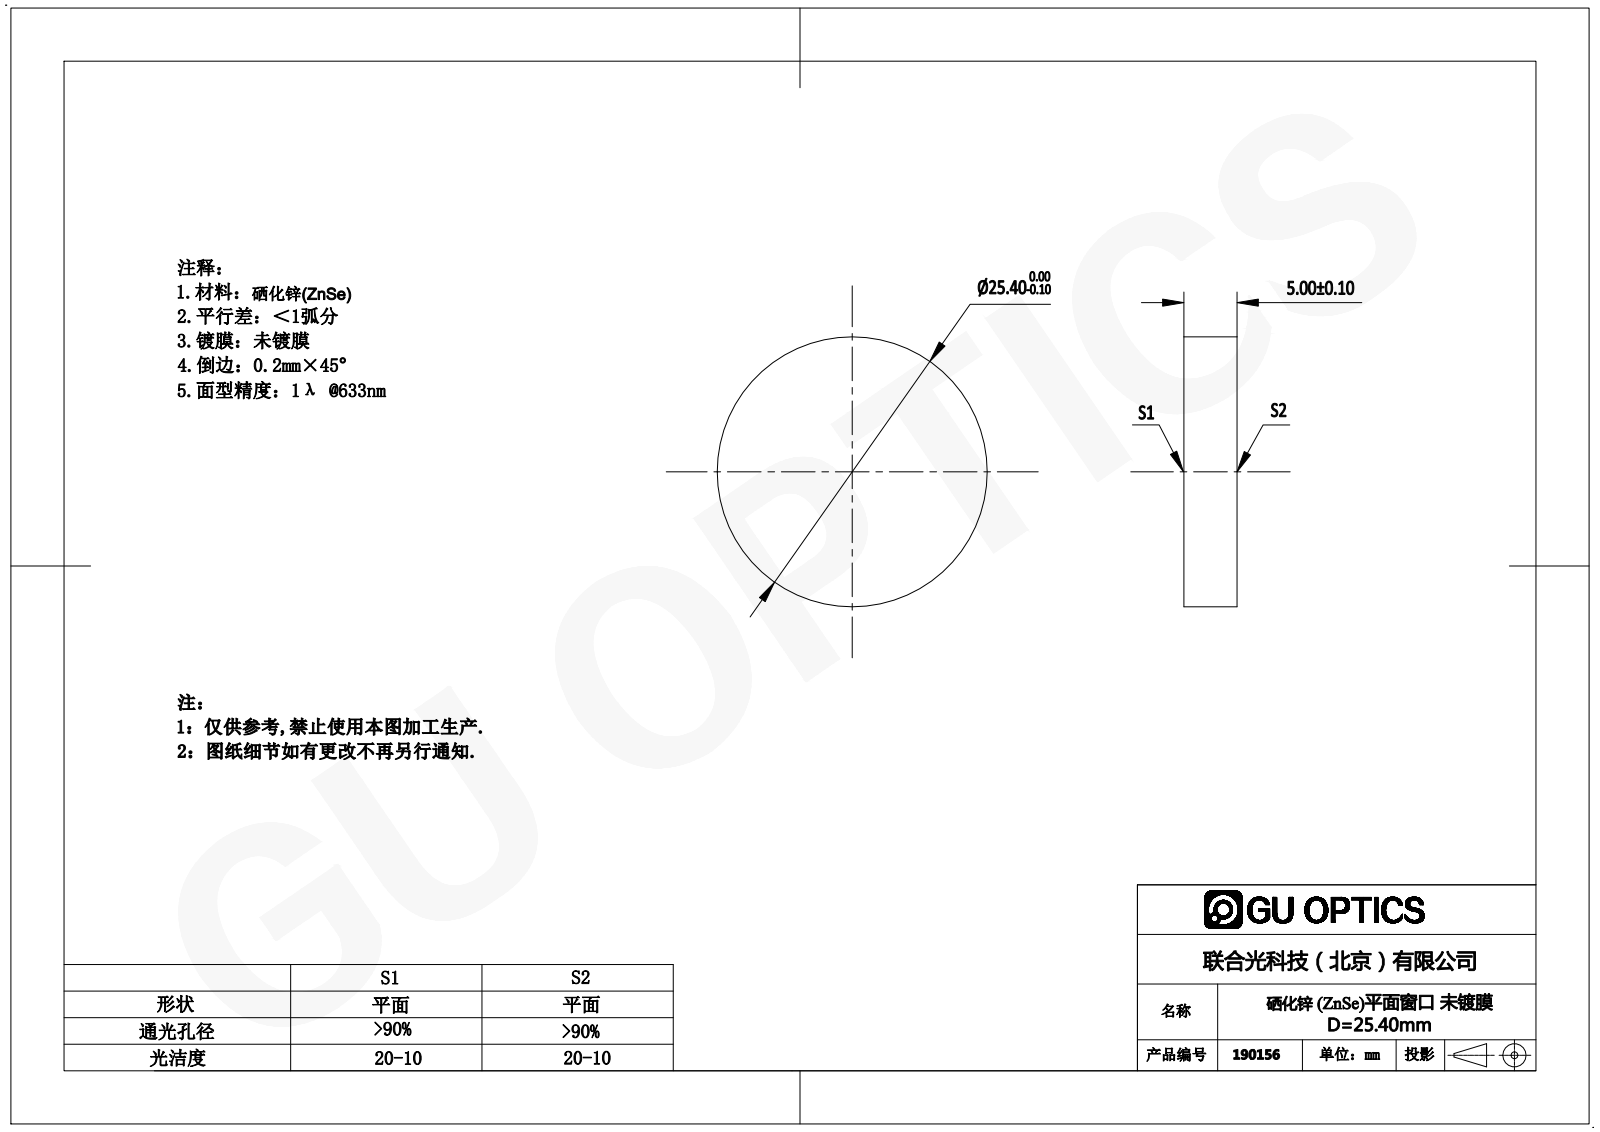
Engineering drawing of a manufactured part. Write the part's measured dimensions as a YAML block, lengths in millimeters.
part_name: "190156"
step_written_by: "SolidWorks 2016 (AUTOMOTIVE_DESIGN)"
units: millimeters
bodies: {solids: 1, faces: 4, planar: 2, cylindrical: 2, other: 0}
overall_size: [25.4, 25.4, 5]
volume: 2534
surface_area: 1412
round_bosses_or_shafts:
  - {diameter: 25.4, count: 1}
face_to_face_distances: [5]
